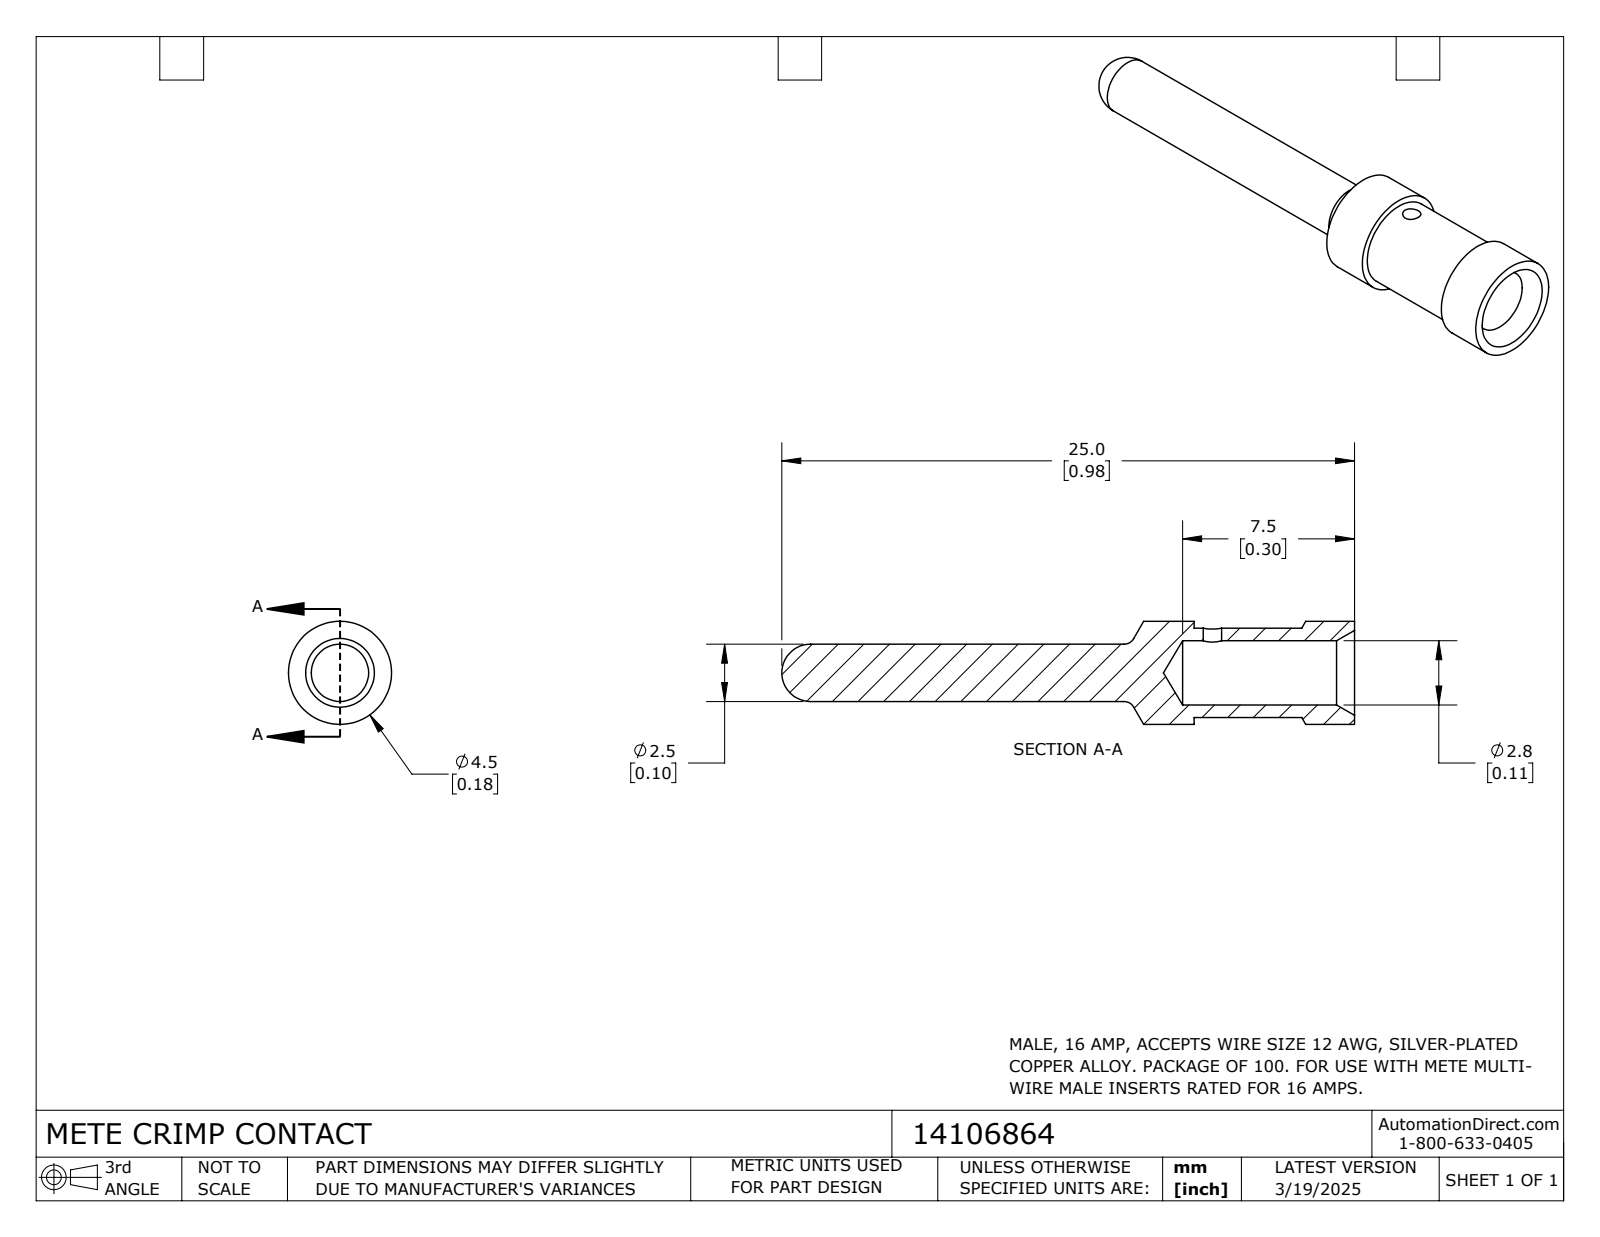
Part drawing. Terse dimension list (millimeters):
name: 14106864
written by: SolidWorks 2024 (CONFIG_CONTROL_DESIGN)
unit: mm
bodies: 1 solid, 26 faces (2 planar, 12 cylindrical, 12 other)
size: 25 × 4.5 × 4.5
volume: 156 mm³; area: 340 mm²
holes: 1× ⌀0.8, 1× ⌀2.8
bosses: 1× ⌀4.5, 1× ⌀3.9, 1× ⌀2.5
face distances: 7
